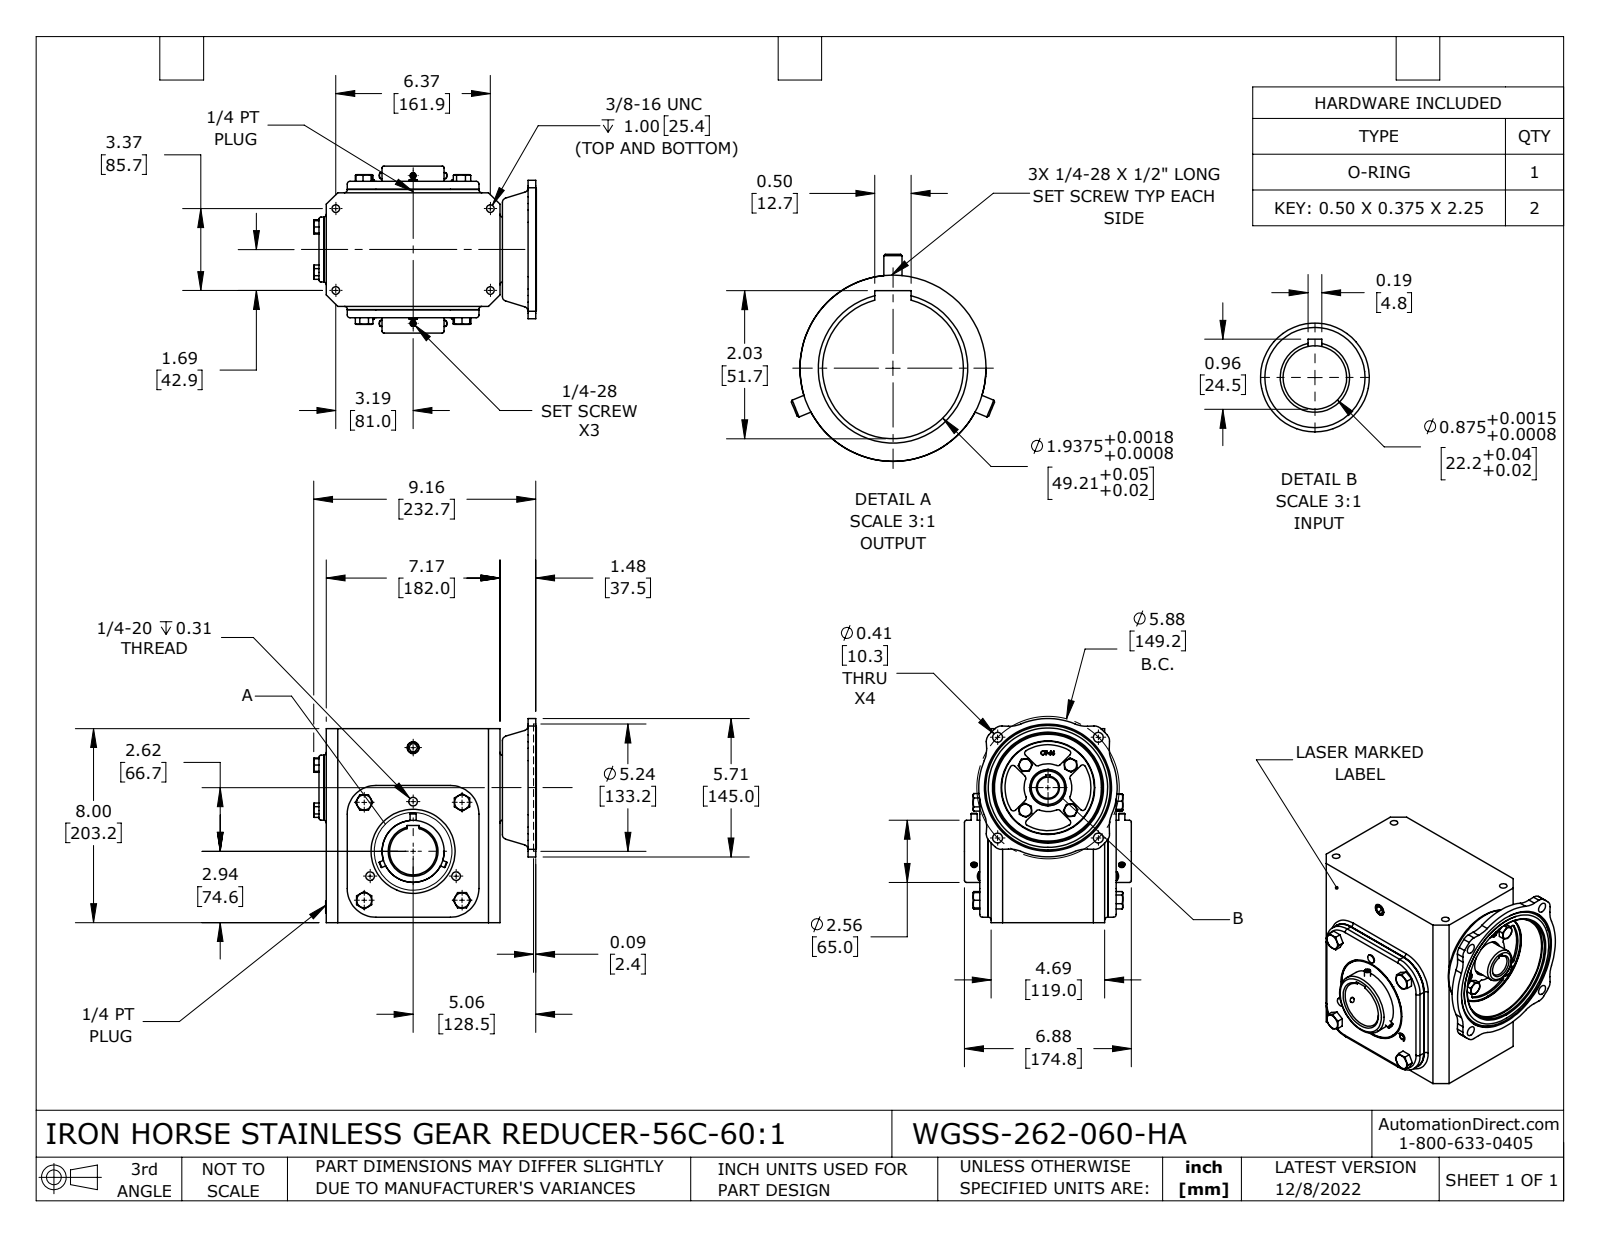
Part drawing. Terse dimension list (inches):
name: WGSS-262-060-HA
written by: SolidWorks 2021 (CONFIG_CONTROL_DESIGN)
unit: in
bodies: 45 solids, 1776 faces (625 planar, 516 cylindrical, 635 other)
size: 9.184 × 8.417 × 6.882
volume: 121.8 in³; area: 1 055 in²
holes: 6× ⌀0.213, 4× ⌀0.268, 4× ⌀0.313, 4× ⌀0.335, 4× ⌀0.354, 4× ⌀0.406, 4× ⌀0.433, 3× ⌀0.201, 2× ⌀0.079, 1× ⌀0.875, 1× ⌀0.941, 1× ⌀1.102
bosses: 6× ⌀0.25, 4× ⌀0.709, 4× ⌀0.394, 4× ⌀0.315, 3× ⌀0.354, 3× ⌀0.205, 1× ⌀4.921, 1× ⌀4.409
rounds: 40× R0.118, 12× R0.394, 12× R1.181, 8× R0.039, 8× R0.197, 6× R0.079, 4× R0.236, 2× R0.019
face distances: 0.197, 0.335, 4.961, 0.669, 7.803, 0.472, 5.157, 4.488, 0.138, 6.969
hole spacings: 3.22, 1.319, 1.619, 1.865, 2.855, 2.937, 3.465, 4.037
